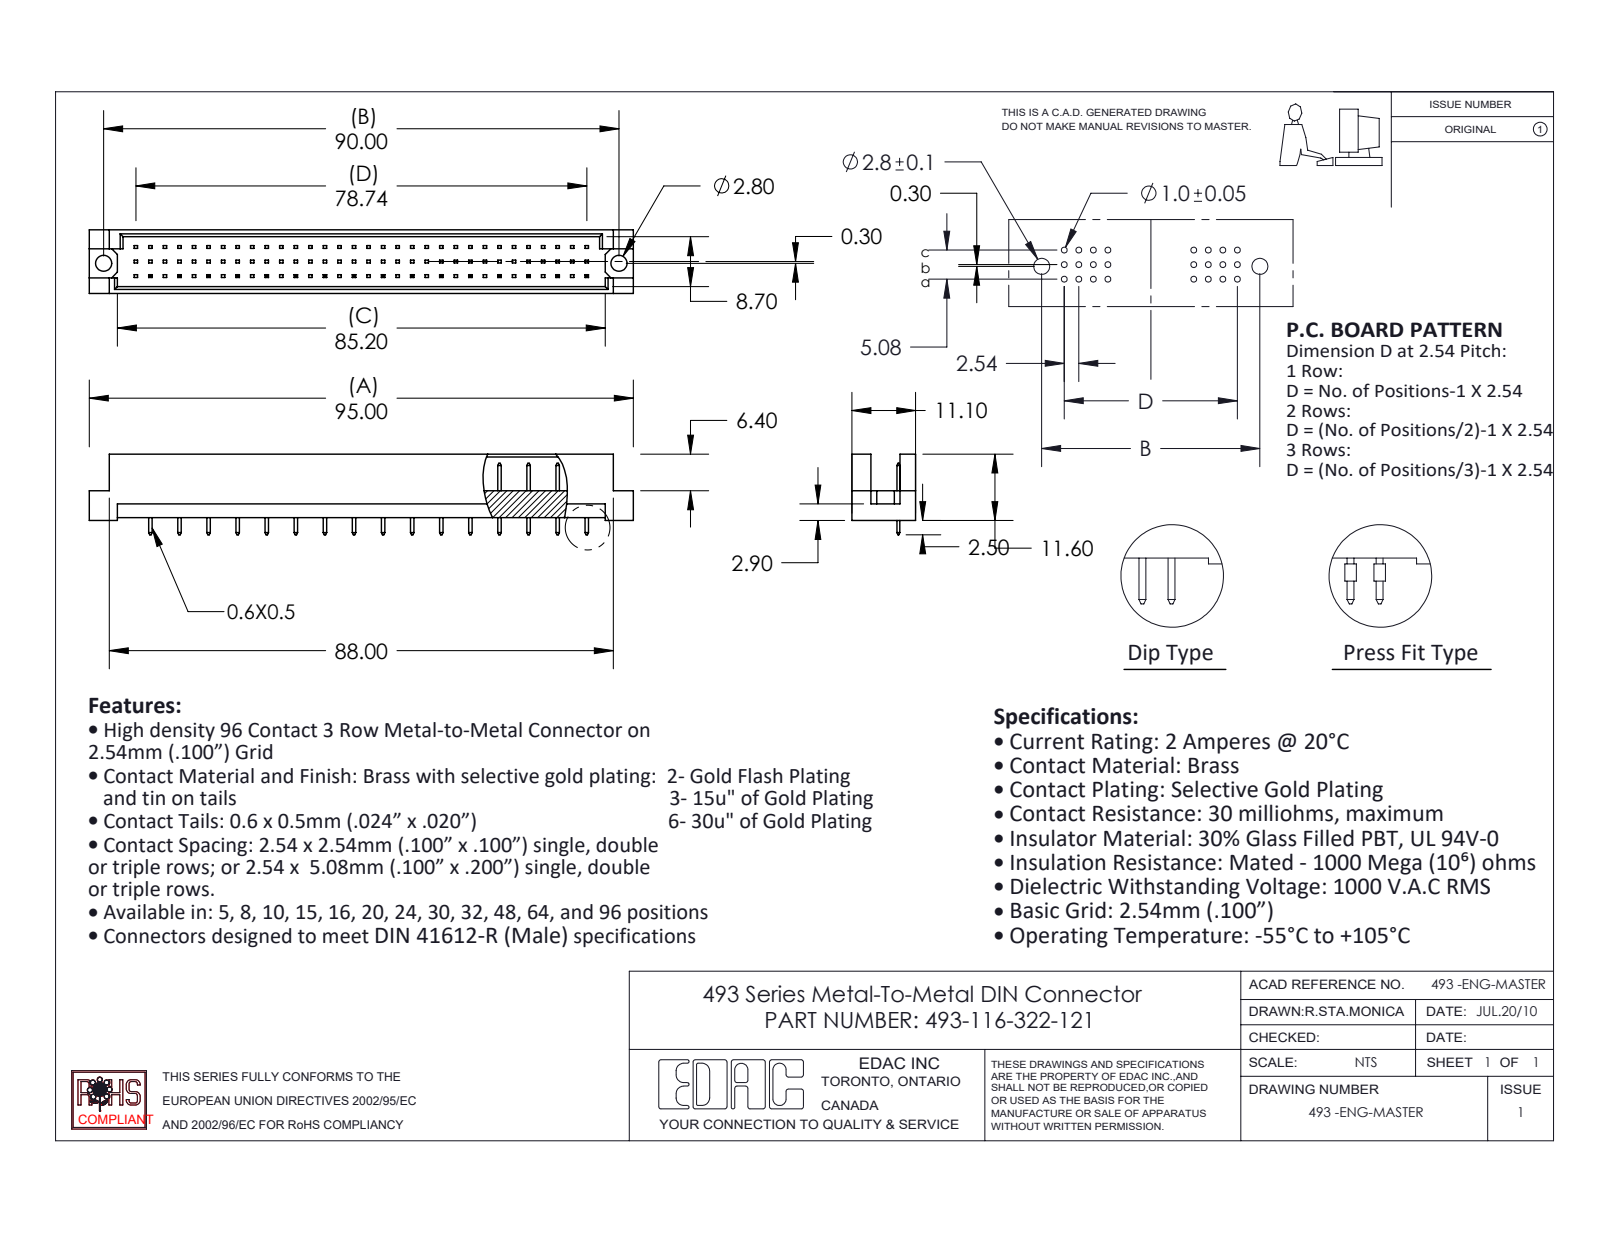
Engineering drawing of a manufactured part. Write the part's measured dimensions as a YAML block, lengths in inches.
part_name: "493-116-322-621; 493-290_22; 493 Part_96"
step_written_by: "SolidWorks 2020 (CONFIG_CONTROL_DESIGN)"
units: inches
bodies: {solids: 17, faces: 660, planar: 656, cylindrical: 4, other: 0}
overall_size: [3.74, 0.555, 0.437]
volume: 0.349
surface_area: 10.71
round_holes:
  - {diameter: 0.11, count: 2}
face_to_face_distances: [0.047, 0.39, 0.437, 0.343, 0.185, 0.02, 0.2, 0.1, 0.109, 0.128]
hole_center_spacings: [3.543]
